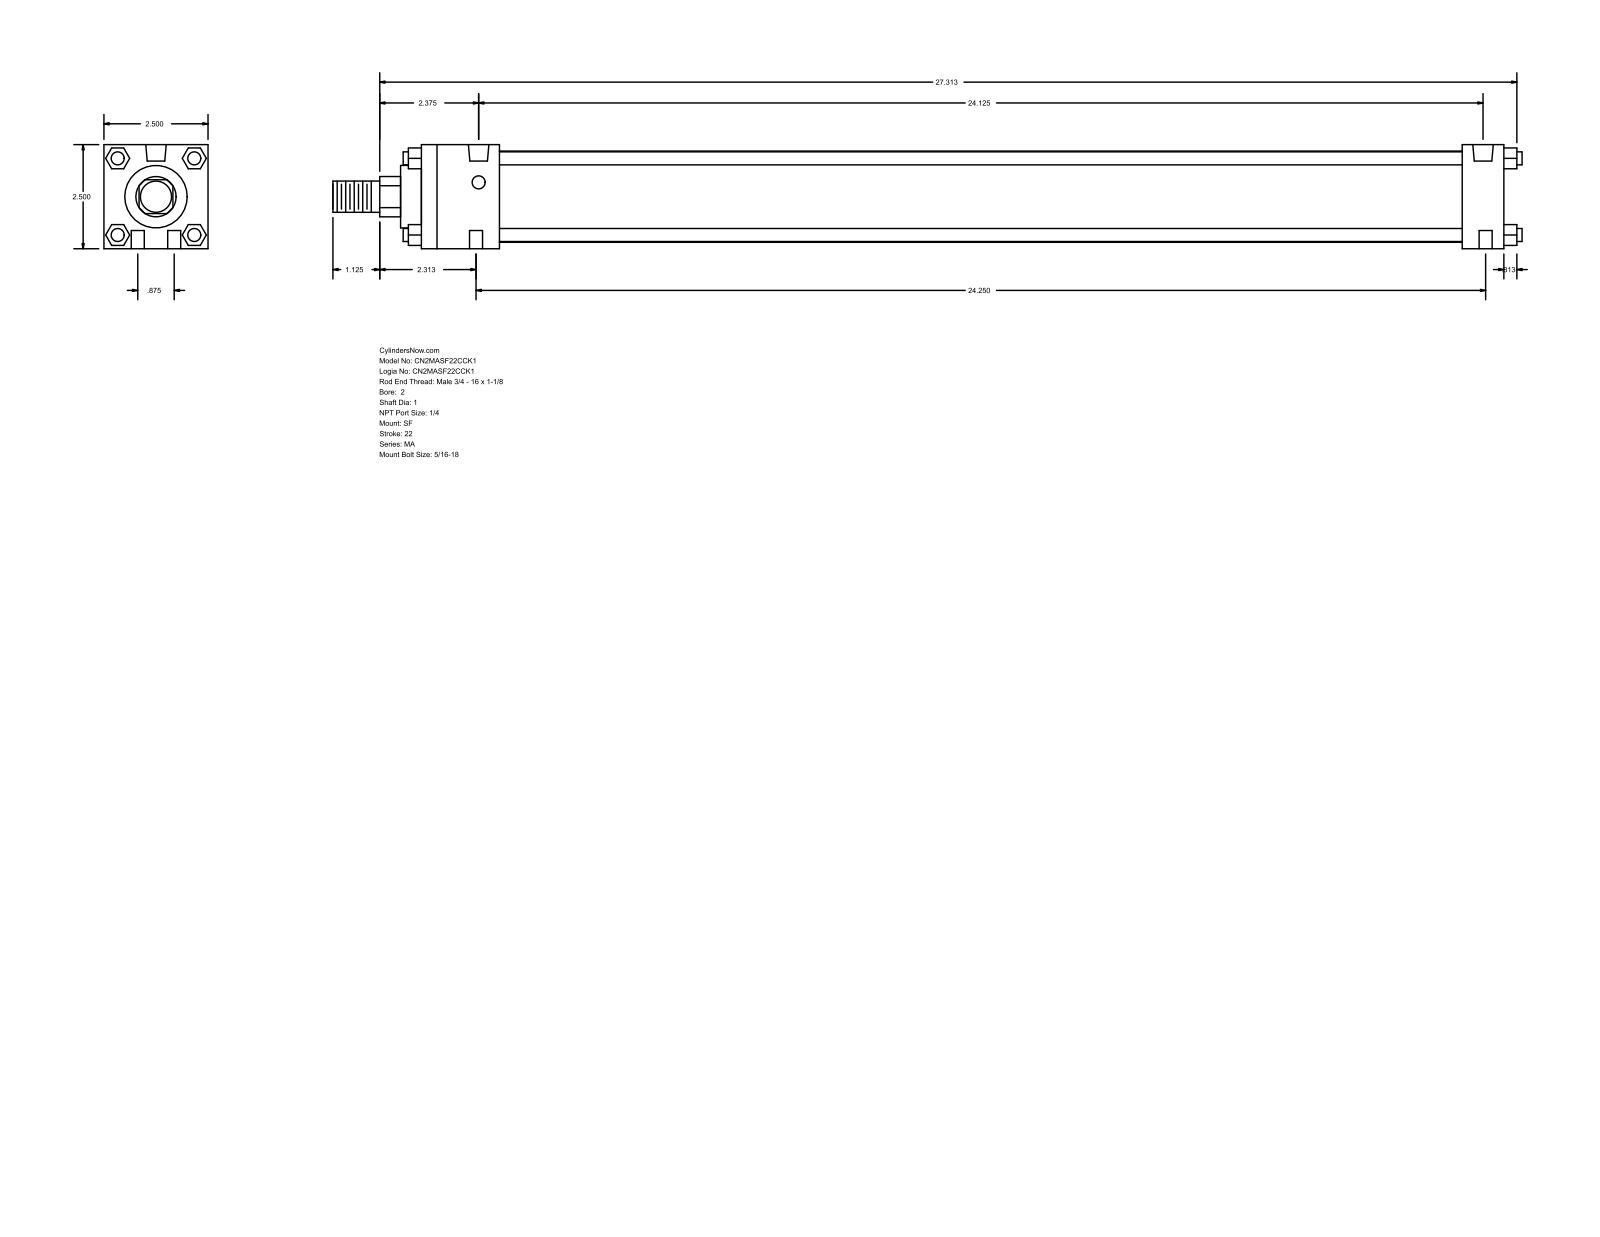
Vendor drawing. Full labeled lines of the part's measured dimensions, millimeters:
Part name (STEP PRODUCT): MA_SF__0200_1
STEP written by: GSSL Pune (CONFIG_CONTROL_DESIGN)
Units: millimetres
Bodies: 0 solids, 124 faces (94 planar, 30 cylindrical, 0 other)
Overall size (bounding box): 725.49 × 63.5 × 63.5
Round holes (diameter × count): ⌀7.94 ×6, ⌀12.49 ×2
Round bosses / shafts (diameter × count): ⌀7.94 ×4, ⌀55.63 ×1, ⌀38.1 ×1, ⌀25.4 ×1, ⌀19.05 ×1
Partial cylindrical surfaces — rounded edges, fillets, slot ends (radius × count): R12.29 ×1
Main face-to-face distances: 63.5, 660.4, 12.7, 25.4, 635, 47.63, 587.37, 612.77, 40.47, 23.37
Hole centre spacings: 11.22, 614.46, 22.22, 612.77, 615.95, 616.35
